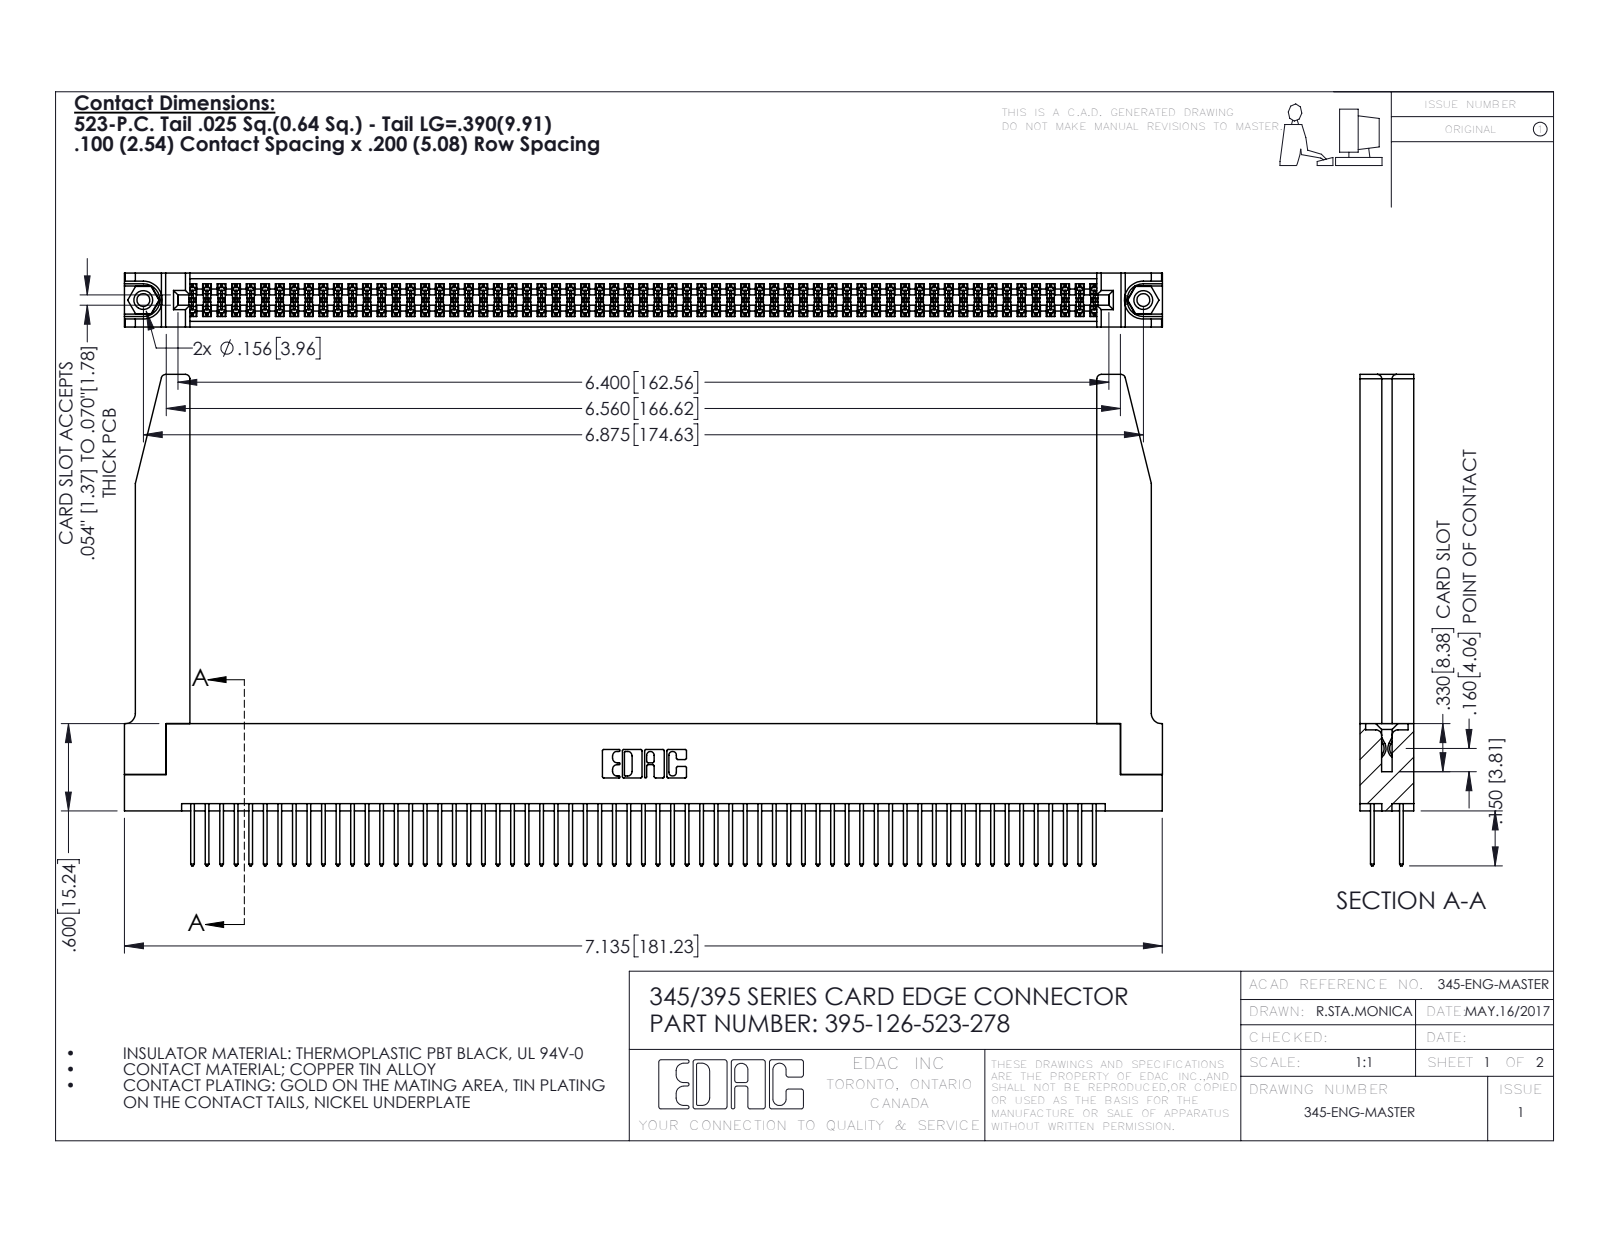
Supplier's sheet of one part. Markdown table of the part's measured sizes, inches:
| quantity | value |
| --- | --- |
| part name | 345-220-078_345-220-078; 345 Part_Flush Mounting Lugs - 0.156 Dia-TH; 395-126-523-278; 345-250-001_345-250-001-102 (+1 more) |
| STEP written by | SolidWorks 2016 (CONFIG_CONTROL_DESIGN) |
| units | inches |
| bodies | 131 solids, 6660 faces (4380 planar, 2228 cylindrical, 52 other) |
| overall size | 7.136 × 3.377 × 0.37 |
| volume | 1.576 in³ |
| surface area | 54.41 in² |
| round holes (diameter × count) | 0.089 × 2, 0.125 × 2, 0.156 × 2, 0.064 × 1 |
| round bosses / shafts (diameter × count) | 0.155 × 2 |
| partial cylindrical surfaces (radius × count) | 0.006 × 189, 0.01 × 126, 0.01 × 22, 0.03 × 8, 0.007 × 6, 0.031 × 6, 0.026 × 3, 0.014 × 2 |
| main face-to-face distances | 0.072, 0.298, 0.37, 0.2, 0.098, 0.272, 0.025, 0.225, 0.175, 0.148 |
| hole center spacings | 0.27, 6.639, 6.875 |
